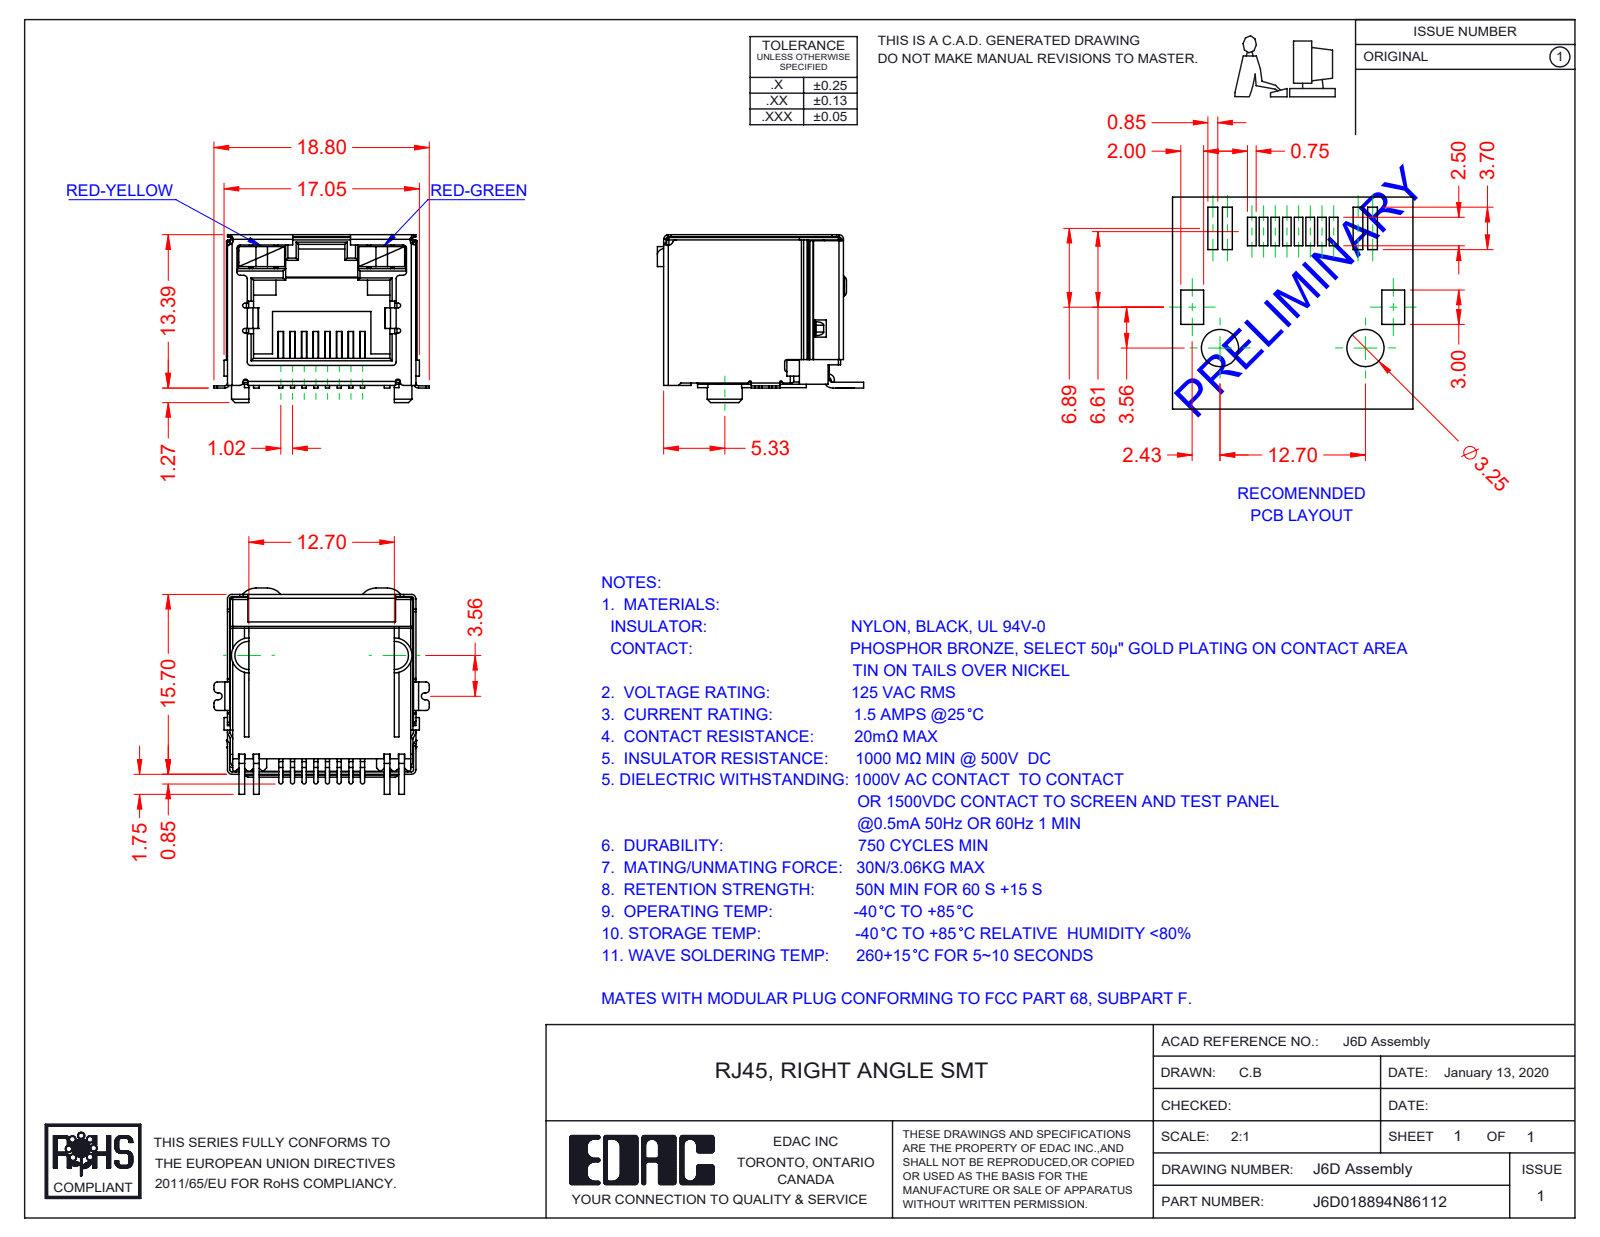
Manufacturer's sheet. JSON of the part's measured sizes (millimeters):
{"part_name": "6D LED LH_8-Red-Yellow; 6D Insulator; 6D Shield_LED - No EMI; 6D LED RH_6-Red-Green (+2 more)", "step_written_by": "SolidWorks 2016 (CONFIG_CONTROL_DESIGN)", "units": "millimeters", "bodies": {"solids": 12, "faces": 899, "planar": 646, "cylindrical": 220, "other": 33}, "overall_size": [18.8, 18, 14.65], "volume_mm3": 1804, "surface_area_mm2": 4898, "partial_cylinders_radius": [[0.3, 39], [0.2, 37], [0.4, 16], [0.1, 12], [0.15, 8], [0.18, 8], [0.5, 6], [1.5, 5]], "face_to_face_distances": [16, 16.25, 16.2, 2.25, 1, 15.95, 16.05, 12.8, 0.45, 16.45]}
